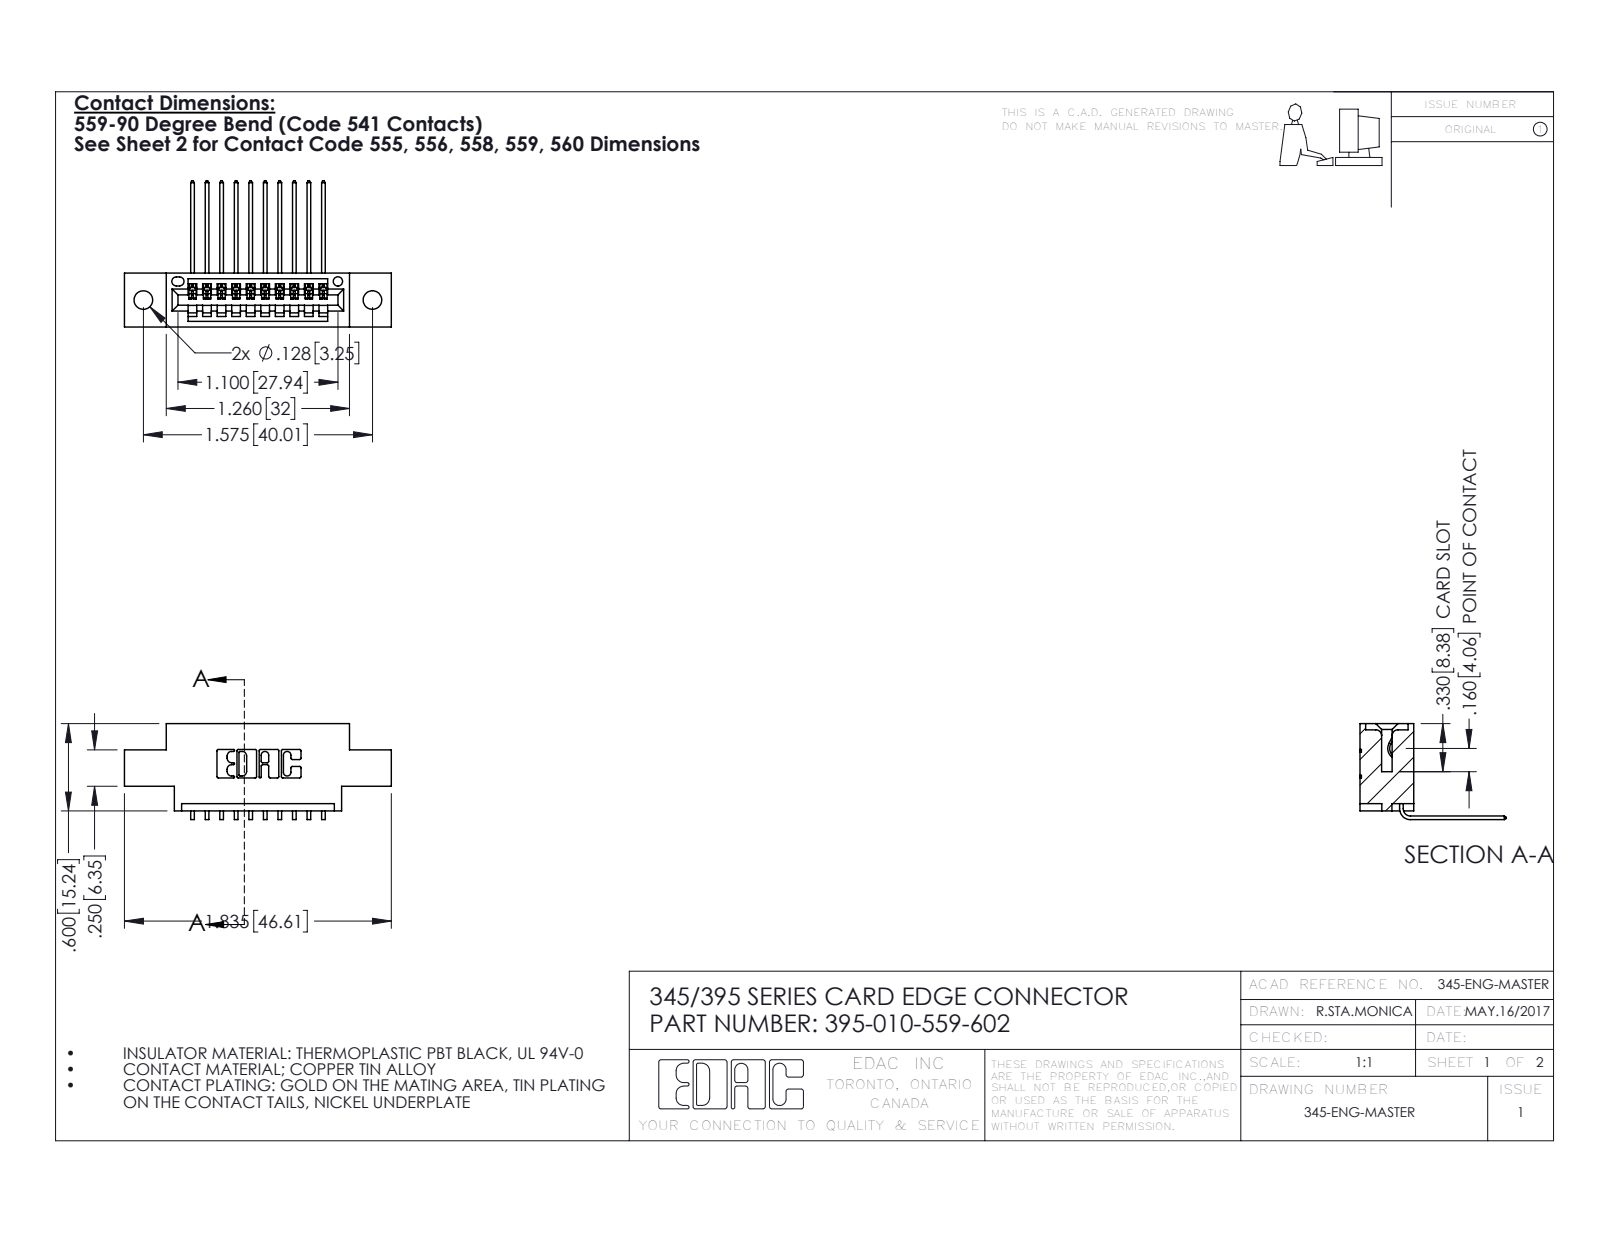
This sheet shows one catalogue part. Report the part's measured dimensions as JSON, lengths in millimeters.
{"part_name": "345 Part_0.170 Offset - 0.128 Dia; 395-010-559-602; 345-292-001_558 559 Tail - 1", "step_written_by": "SolidWorks 2016 (CONFIG_CONTROL_DESIGN)", "units": "millimeters", "bodies": {"solids": 11, "faces": 730, "planar": 504, "cylindrical": 226, "other": 0}, "overall_size": [46.6, 25.5, 16.7], "volume_mm3": 4050, "surface_area_mm2": 4995, "round_holes": [[3.3, 2], [1.6, 1]], "partial_cylinders_radius": [[0.3, 22], [0.2, 20], [0.2, 6], [0.8, 6], [0.7, 3], [0.8, 2], [1, 2], [0.4, 1]], "face_to_face_distances": [9.4, 1.8, 7.6, 5.1, 2.5, 2.5, 6.9, 0.6, 15.2, 1.5], "hole_center_spacings": [6.9, 34.1, 40]}
